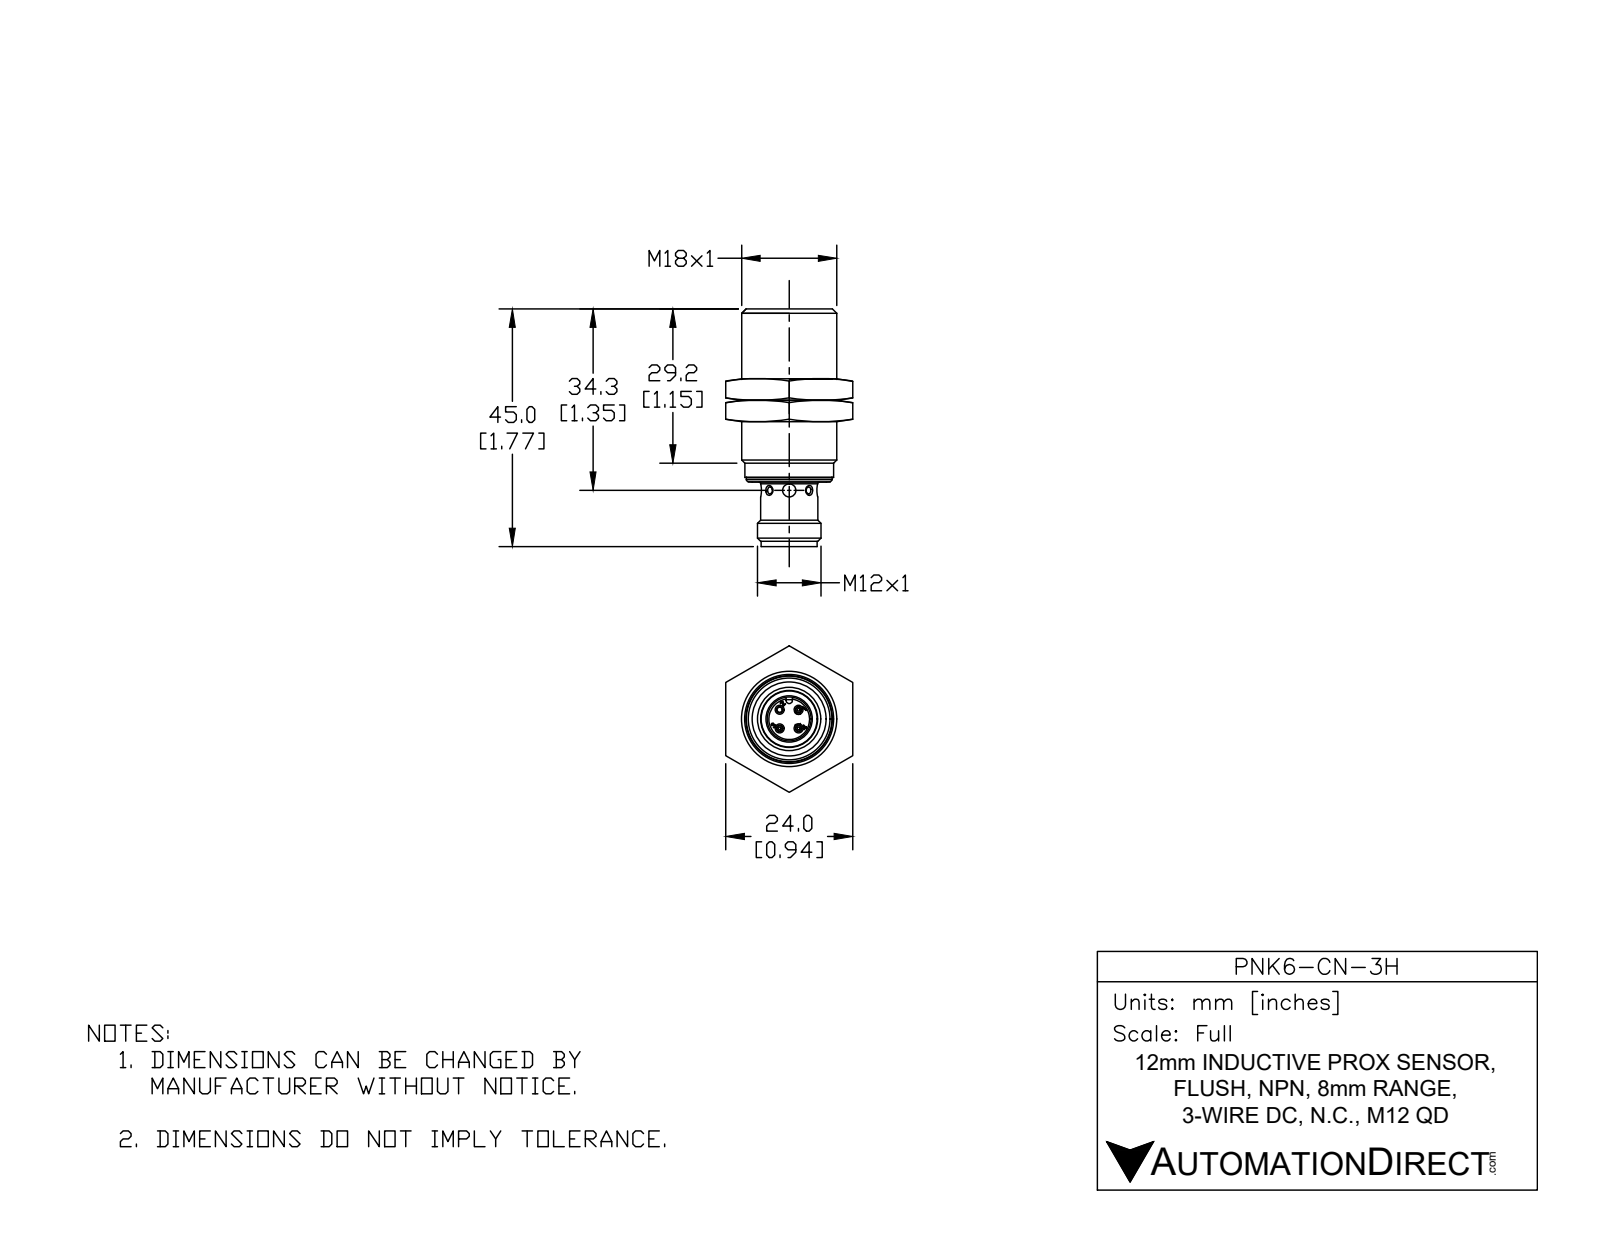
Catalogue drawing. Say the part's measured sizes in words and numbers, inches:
The part is named "PNK6-CN-3H". Its 3-D file was written by "SolidWorks 2017 (AUTOMOTIVE_DESIGN)". It is 1 solid with 476 faces: 118 planar, 129 cylindrical and 229 other. Overall it measures 1.772 by 0.709 by 0.709 inches. Its volume is 0.401 cubic inches and its surface area 7.642 square inches. Round holes: 3 of diameter 0.04, 3 of diameter 0.043, 2 of diameter 0.098, 1 of diameter 0.038, 1 of diameter 0.323, 1 of diameter 0.327, 1 of diameter 0.394, 1 of diameter 0.618. Round bosses or shafts: 9 of diameter 0.039, 1 of diameter 0.709, 1 of diameter 0.661, 1 of diameter 0.642, 1 of diameter 0.638, 1 of diameter 0.616, 1 of diameter 0.472, 1 of diameter 0.425. Partial cylindrical surfaces (rounded edges, fillets, slot ends): 24 of radius 0.004, 6 of radius 0.039, 6 of radius 0.071, 1 of radius 0.024, 1 of radius 0.031. The main face-to-face distances are 0.452, 0.03, 0.422, 1.236, 1.207, 0.785, 1.291, 0.055, 1.262, 0.84. The hole center spacings are 0.098, 0.139, 0.197.
